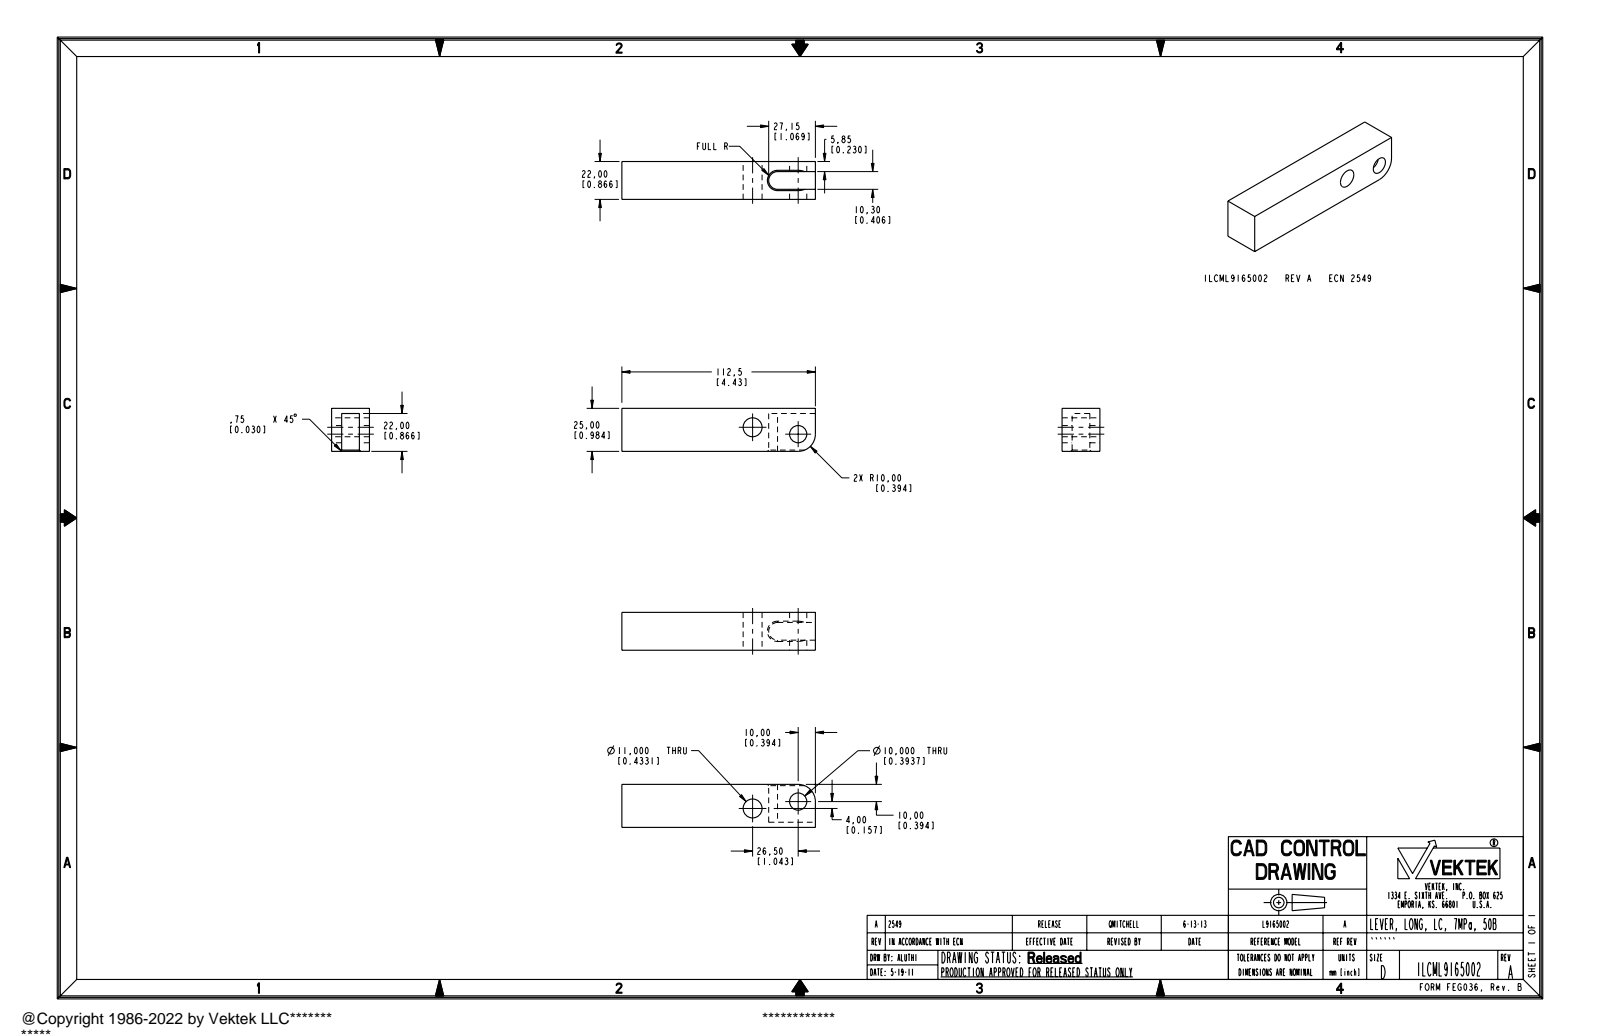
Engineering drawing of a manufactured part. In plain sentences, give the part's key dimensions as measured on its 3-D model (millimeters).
The part is named "ILCML9165002". Its 3-D file was written by "PRO/ENGINEER BY PARAMETRIC TECHNOLOGY CORPORATION, 2007460 (AUTOMOTIVE_DESIGN_CC2)". It is 1 solid with 21 faces: 11 planar, 9 cylindrical and 1 other. Overall it measures 112.5 by 25 by 22 millimeters. Its volume is 52 700 cubic millimeters and its surface area 13 240 square millimeters. Round holes: 1 of diameter 10, 1 of diameter 11. Partial cylindrical surfaces (rounded edges, fillets, slot ends): 1 of radius 5.15, 1 of radius 10. The main face-to-face distances are 22, 25, 5.85, 16.15, 10.3, 3, 112.5. The hole center spacings are 26.8.
